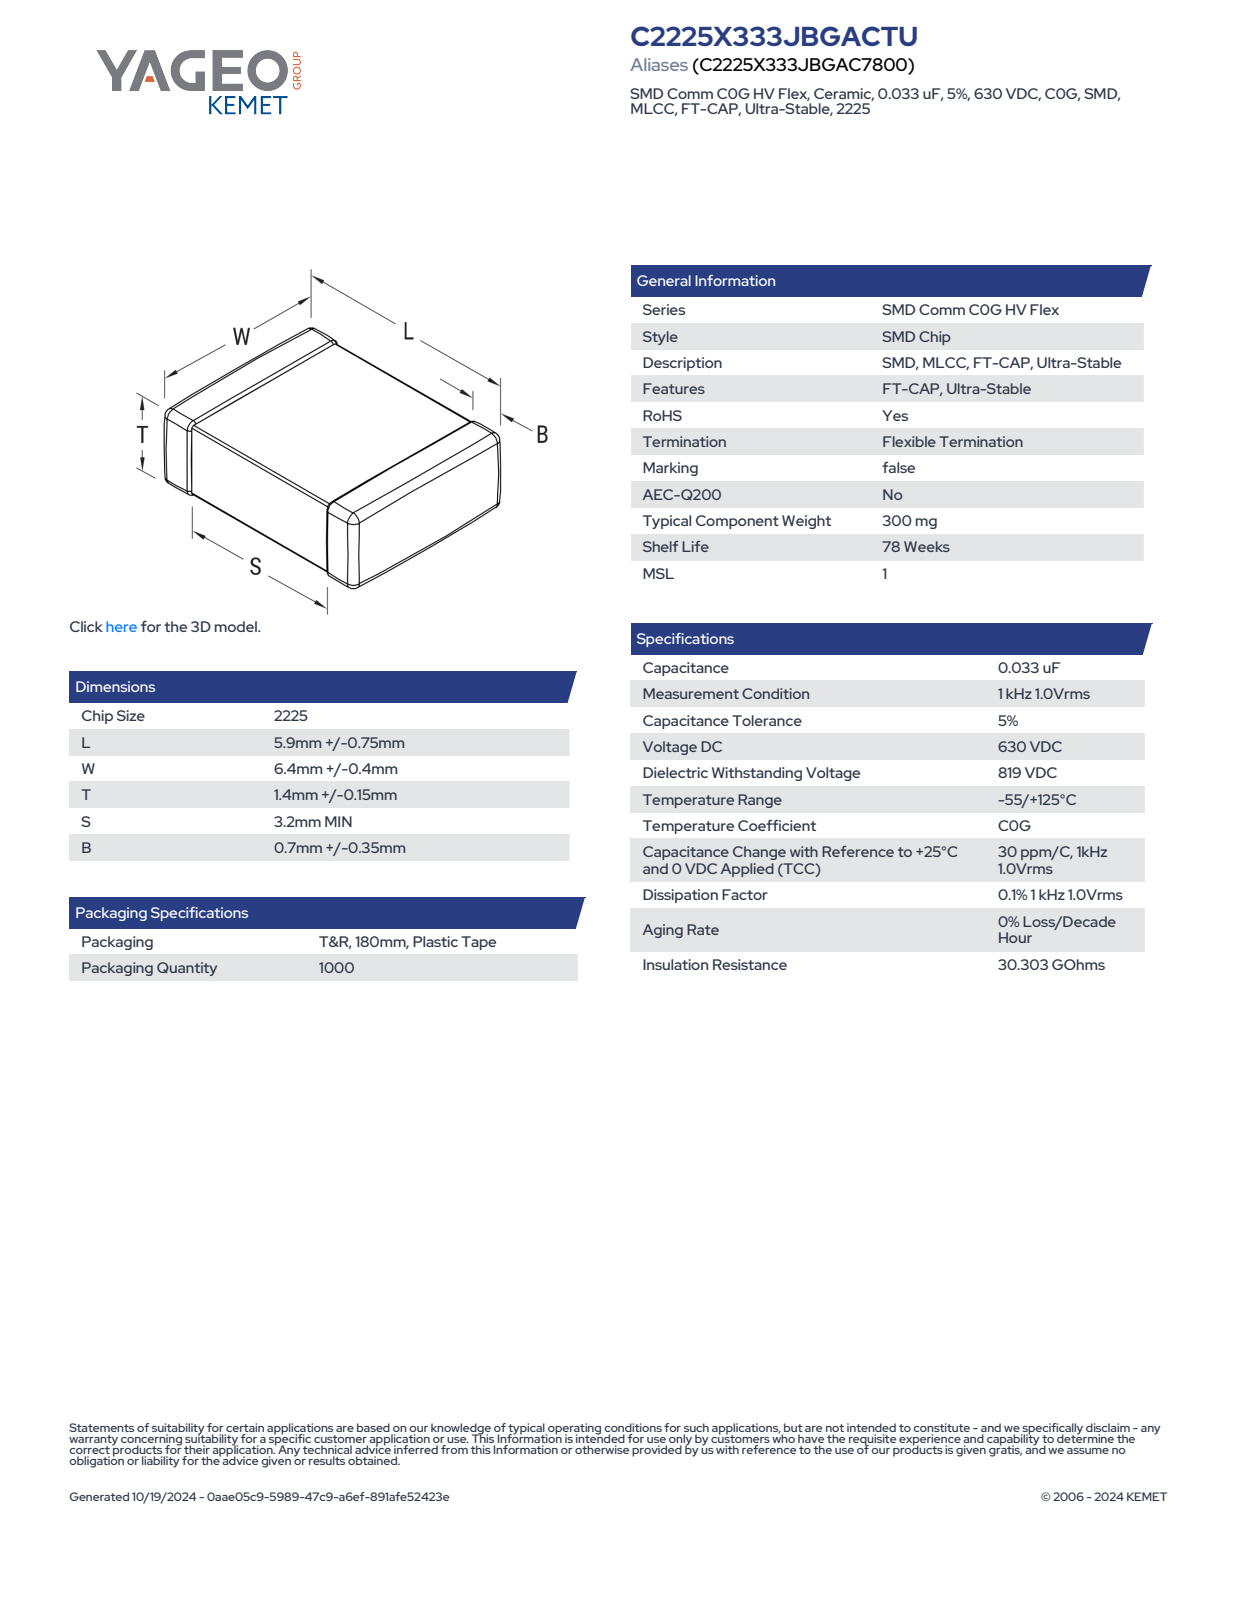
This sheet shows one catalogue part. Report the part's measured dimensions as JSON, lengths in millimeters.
{"part_name": "CCS_CCSTD_2225_L6.65W6.8T1.55B0.7", "step_written_by": "SolidWorks 2021 (AUTOMOTIVE_DESIGN)", "units": "millimeters", "bodies": {"solids": 4, "faces": 121, "planar": 71, "cylindrical": 34, "other": 16}, "overall_size": [6.8, 6.65, 1.55], "volume_mm3": 59, "surface_area_mm2": 132, "partial_cylinders_radius": [[0.14, 24]], "face_to_face_distances": [1.27, 1.41, 1.55, 6.65, 6.52, 6.66, 6.8, 1, 2.59, 4.06]}
